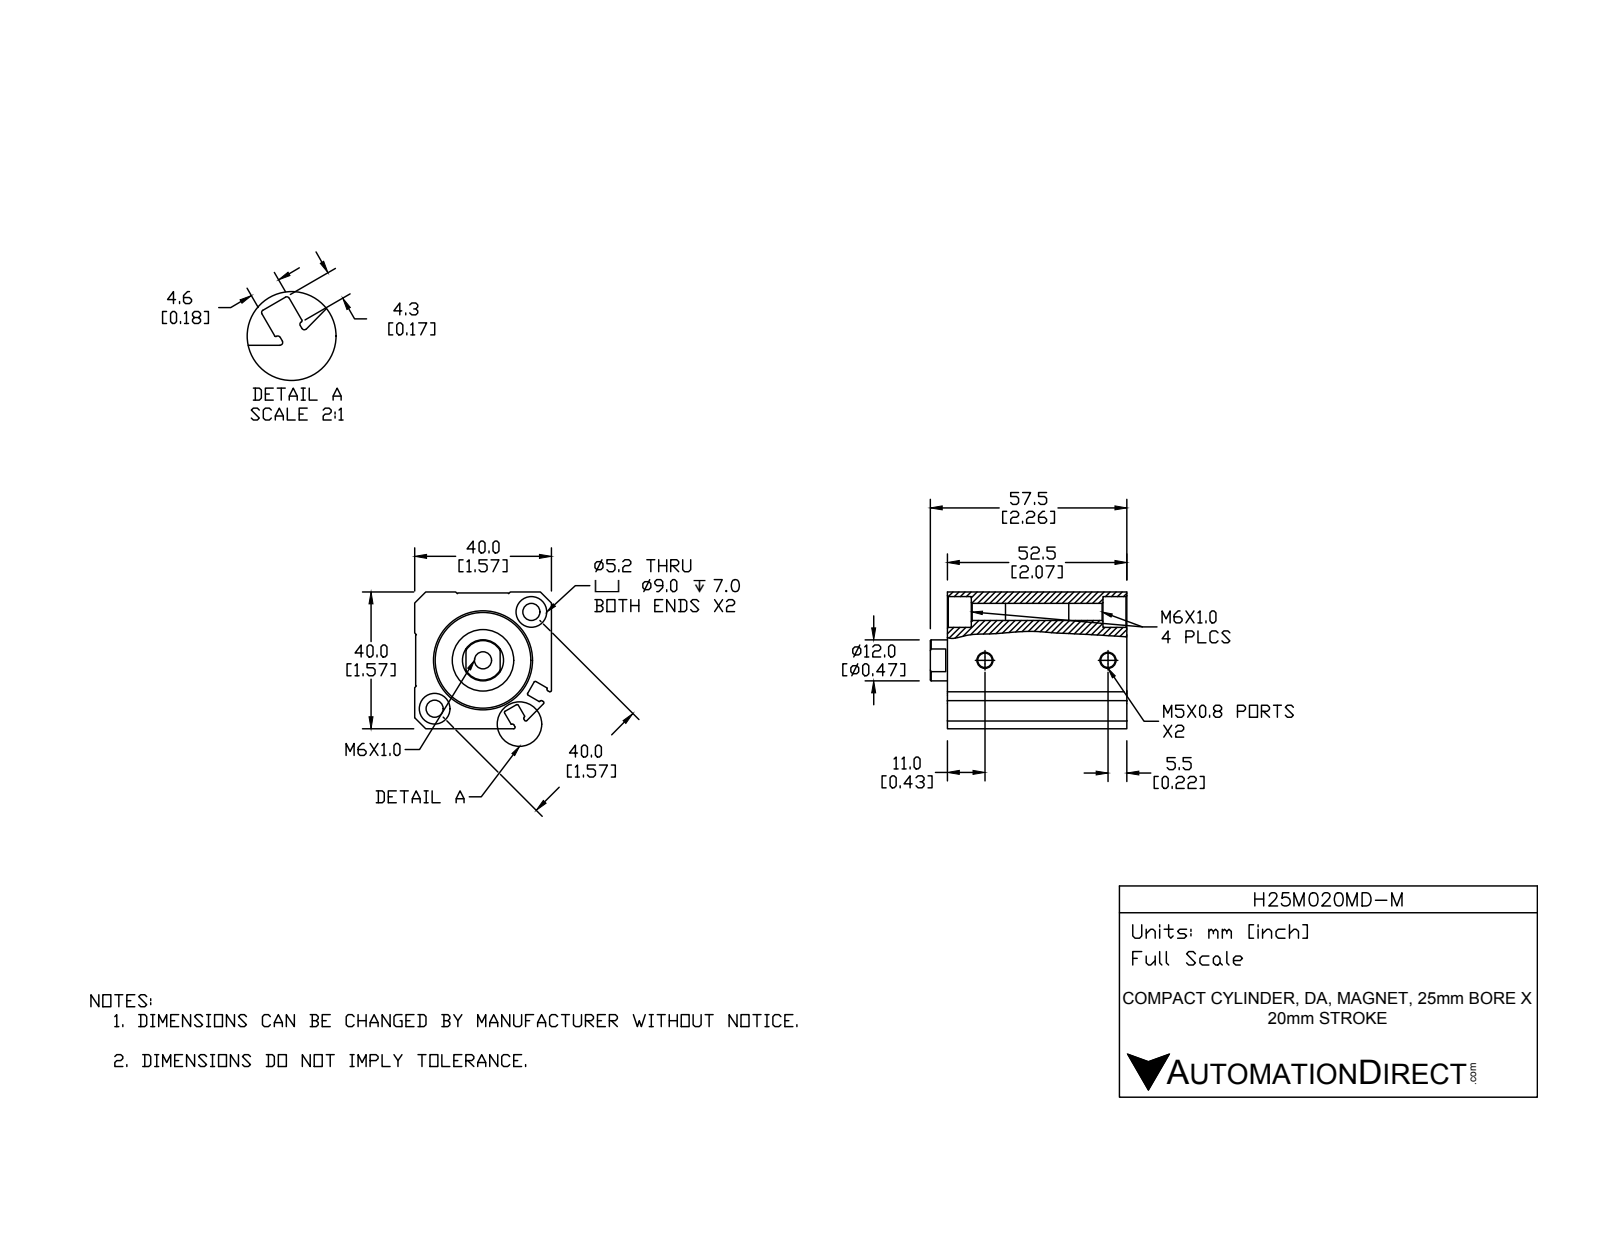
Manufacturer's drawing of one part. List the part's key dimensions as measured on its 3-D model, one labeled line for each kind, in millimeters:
Part name (STEP PRODUCT): H25M020MD-M-BODY; H25M020MD-M; H25M020MD-M-PISTON
STEP written by: SolidWorks 2015 (CONFIG_CONTROL_DESIGN)
Units: millimetres
Bodies: 2 solids, 141 faces (53 planar, 55 cylindrical, 33 other)
Overall size (bounding box): 57.5 × 40 × 40
Volume: 64 578 mm³ · Surface area: 22 634 mm²
Round holes (diameter × count): ⌀5 ×3, ⌀4.2 ×2, ⌀9 ×2, ⌀12 ×1, ⌀16 ×1, ⌀25 ×1, ⌀28 ×1
Round bosses / shafts (diameter × count): ⌀18 ×1, ⌀14 ×1
Partial cylindrical surfaces — rounded edges, fillets, slot ends (radius × count): R0.4 ×12, R0.2 ×4
Main face-to-face distances: 40, 39.7, 4, 52.5, 48.5, 1.4, 2.6, 51.1, 41.5, 17
Hole centre spacings: 20, 36, 39.99
